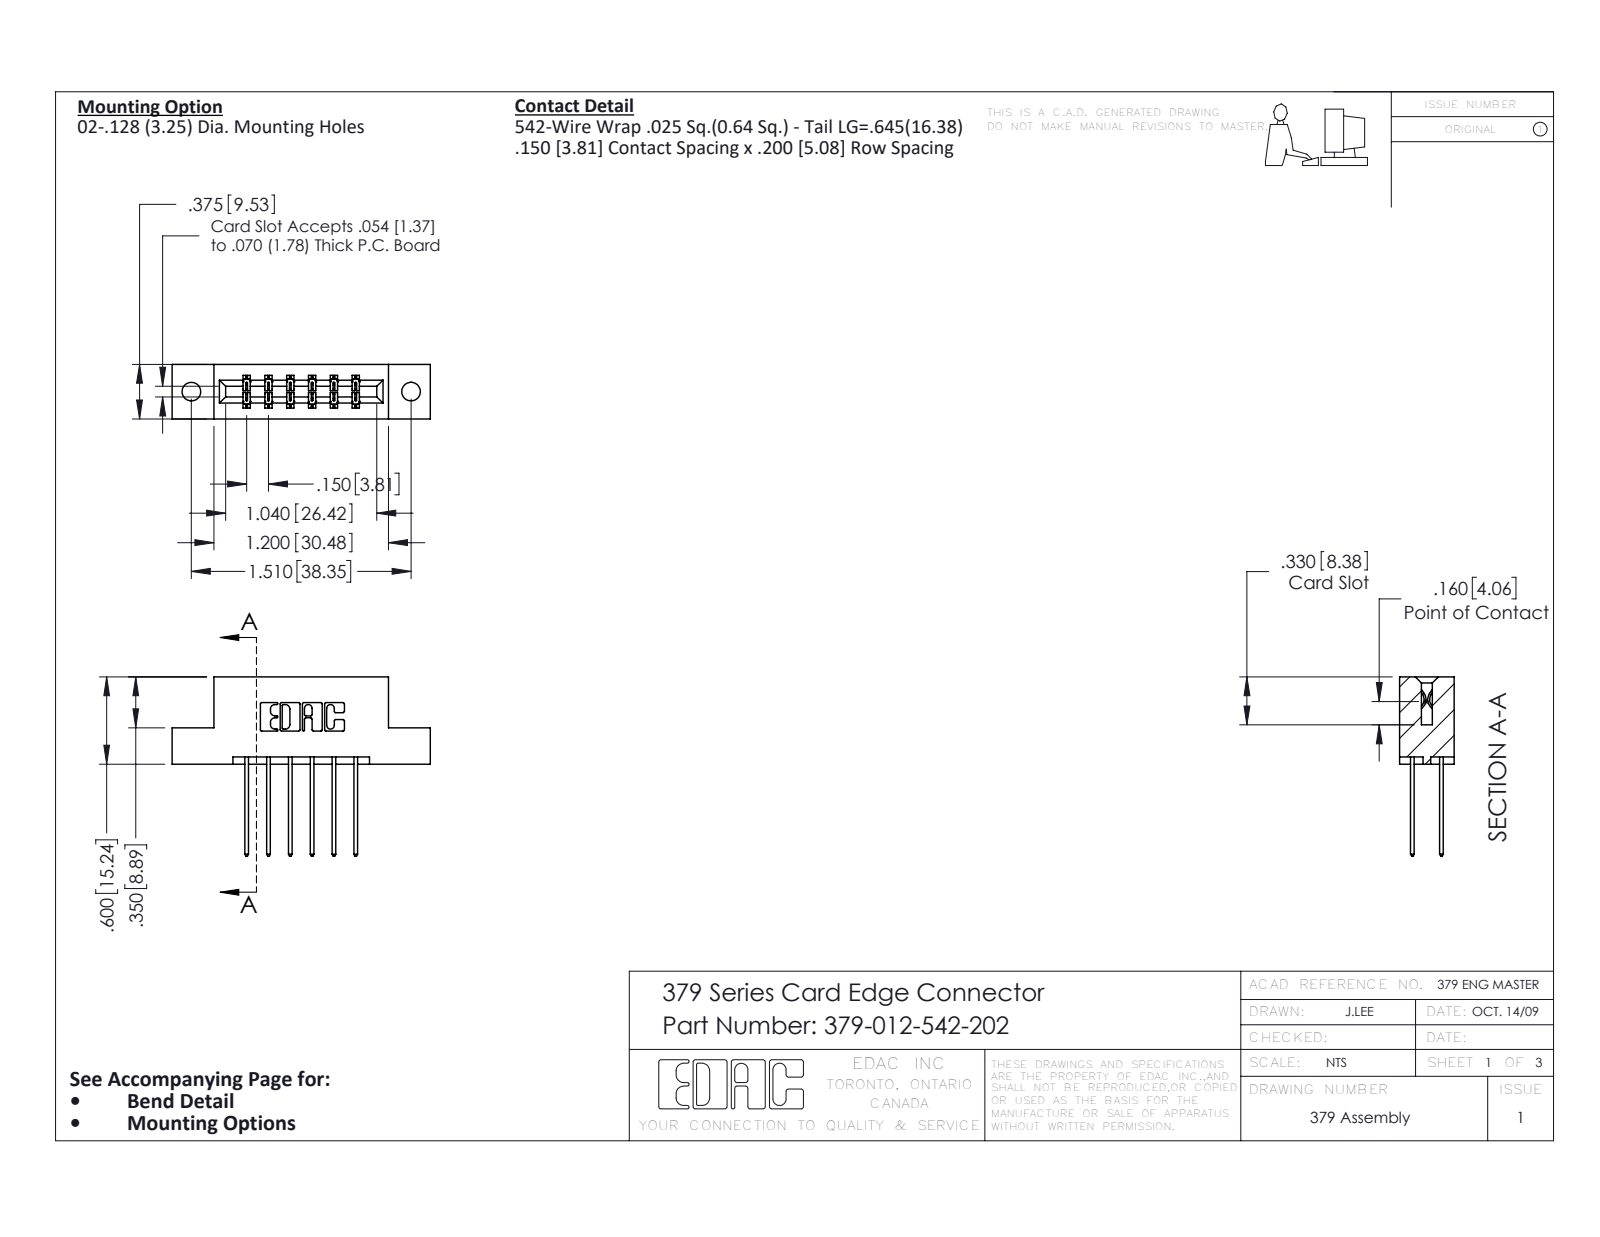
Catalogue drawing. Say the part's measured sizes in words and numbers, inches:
The part is named "379-012-542-202; 379 Part_Flush - .128 Dia; 345-292-001_345-293-142". Its 3-D file was written by "SolidWorks 2016 (CONFIG_CONTROL_DESIGN)". It is 13 solids with 738 faces: 502 planar, 236 cylindrical and 0 other. Overall it measures 1.775 by 1.232 by 0.375 inches. Its volume is 0.266 cubic inches and its surface area 7.099 square inches. Round holes: 2 of diameter 0.128. Partial cylindrical surfaces (rounded edges, fillets, slot ends): 22 of radius 0.01, 18 of radius 0.006, 12 of radius 0.01, 6 of radius 0.007, 6 of radius 0.031, 3 of radius 0.026, 2 of radius 0.014, 2 of radius 0.022. The main face-to-face distances are 0.3, 0.2, 0.15, 0.1, 0.375, 0.05, 0.075, 0.25, 0.35, 0.55. The hole center spacings are 1.51.
